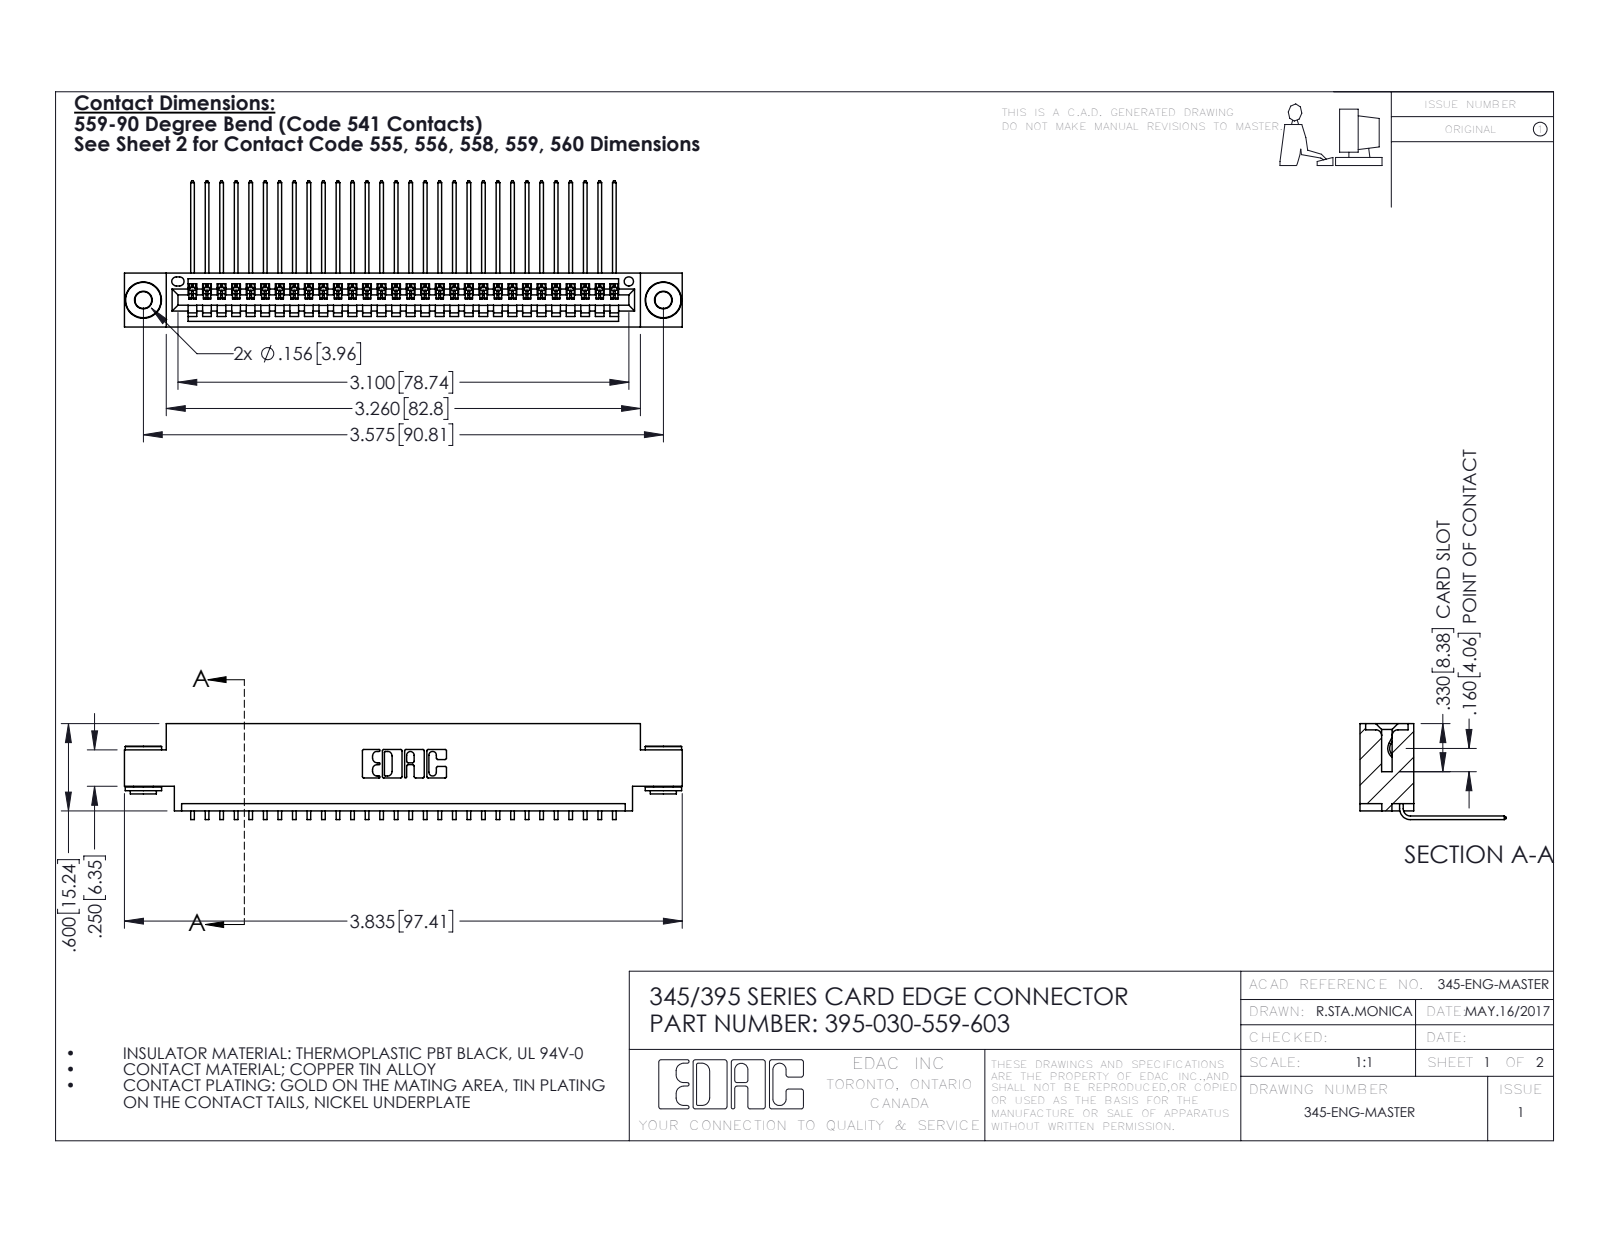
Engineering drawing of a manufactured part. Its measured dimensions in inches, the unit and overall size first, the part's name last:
Units: inches
Overall size (bounding box): 3.835 × 1.005 × 0.659
Round holes (diameter × count): ⌀0.116 ×2, ⌀0.156 ×2, ⌀0.064 ×1
Round bosses / shafts (diameter × count): ⌀0.25 ×2, ⌀0.18 ×2, ⌀0.136 ×2
Partial cylindrical surfaces — rounded edges, fillets, slot ends (radius × count): R0.006 ×60, R0.01 ×22, R0.007 ×6, R0.031 ×6, R0.026 ×3, R0.031 ×2, R0.04 ×2, R0.014 ×1
Main face-to-face distances: 0.072, 0.298, 0.37, 0.2, 0.098, 0.272, 0.025, 0.225, 0.175, 0.149
Hole centre spacings: 0.27, 3.34, 3.575
Volume: 0.559 in³ · Surface area: 20.05 in²
Bodies: 33 solids, 1968 faces (1354 planar, 606 cylindrical, 8 other)
Part name (STEP PRODUCT): 345-292-001_558 559 Tail - 1; 345-250-002_345-250-002-102; 345 Part_0.170 Offset - 0.156 Dia-TH; 395-030-559-603
STEP written by: SolidWorks 2016 (CONFIG_CONTROL_DESIGN)
